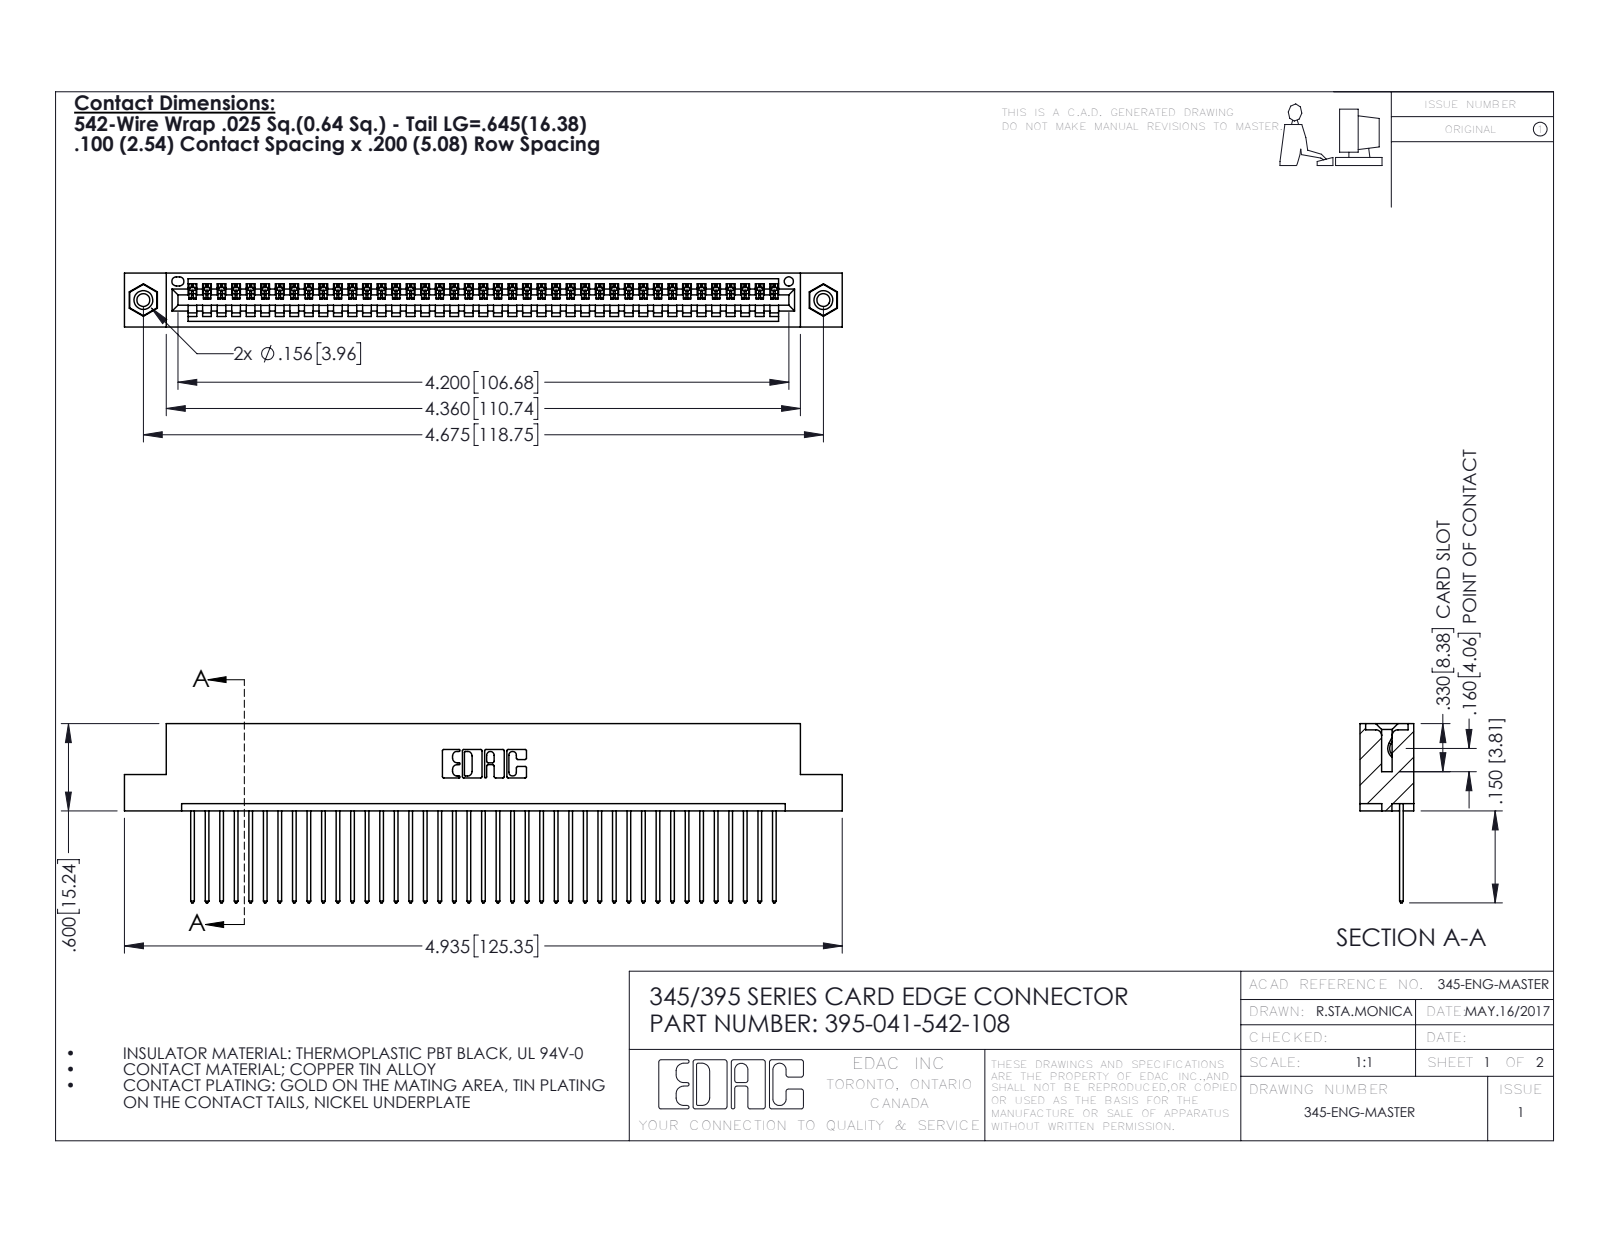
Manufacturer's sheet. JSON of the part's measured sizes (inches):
{"part_name": "395-041-542-108; 345 Part_Flush Mounting Lugs - 0.156 Dia-TI; 345-292-001_345-293-142; 345-250-001_345-250-003-102", "step_written_by": "SolidWorks 2016 (CONFIG_CONTROL_DESIGN)", "units": "inches", "bodies": {"solids": 44, "faces": 2564, "planar": 1752, "cylindrical": 796, "other": 16}, "overall_size": [4.935, 1.232, 0.37], "volume_in3": 0.731, "surface_area_in2": 25.58, "round_holes": [[0.089, 2], [0.125, 2], [0.156, 2], [0.064, 1]], "round_bosses_or_shafts": [[0.155, 2]], "partial_cylinders_radius": [[0.006, 82], [0.01, 82], [0.01, 22], [0.007, 6], [0.031, 6], [0.026, 3], [0.031, 2], [0.04, 2]], "face_to_face_distances": [0.072, 0.298, 0.37, 0.098, 0.272, 0.025, 0.2, 0.225, 0.149, 0.072], "hole_center_spacings": [0.27, 4.439, 4.675]}
